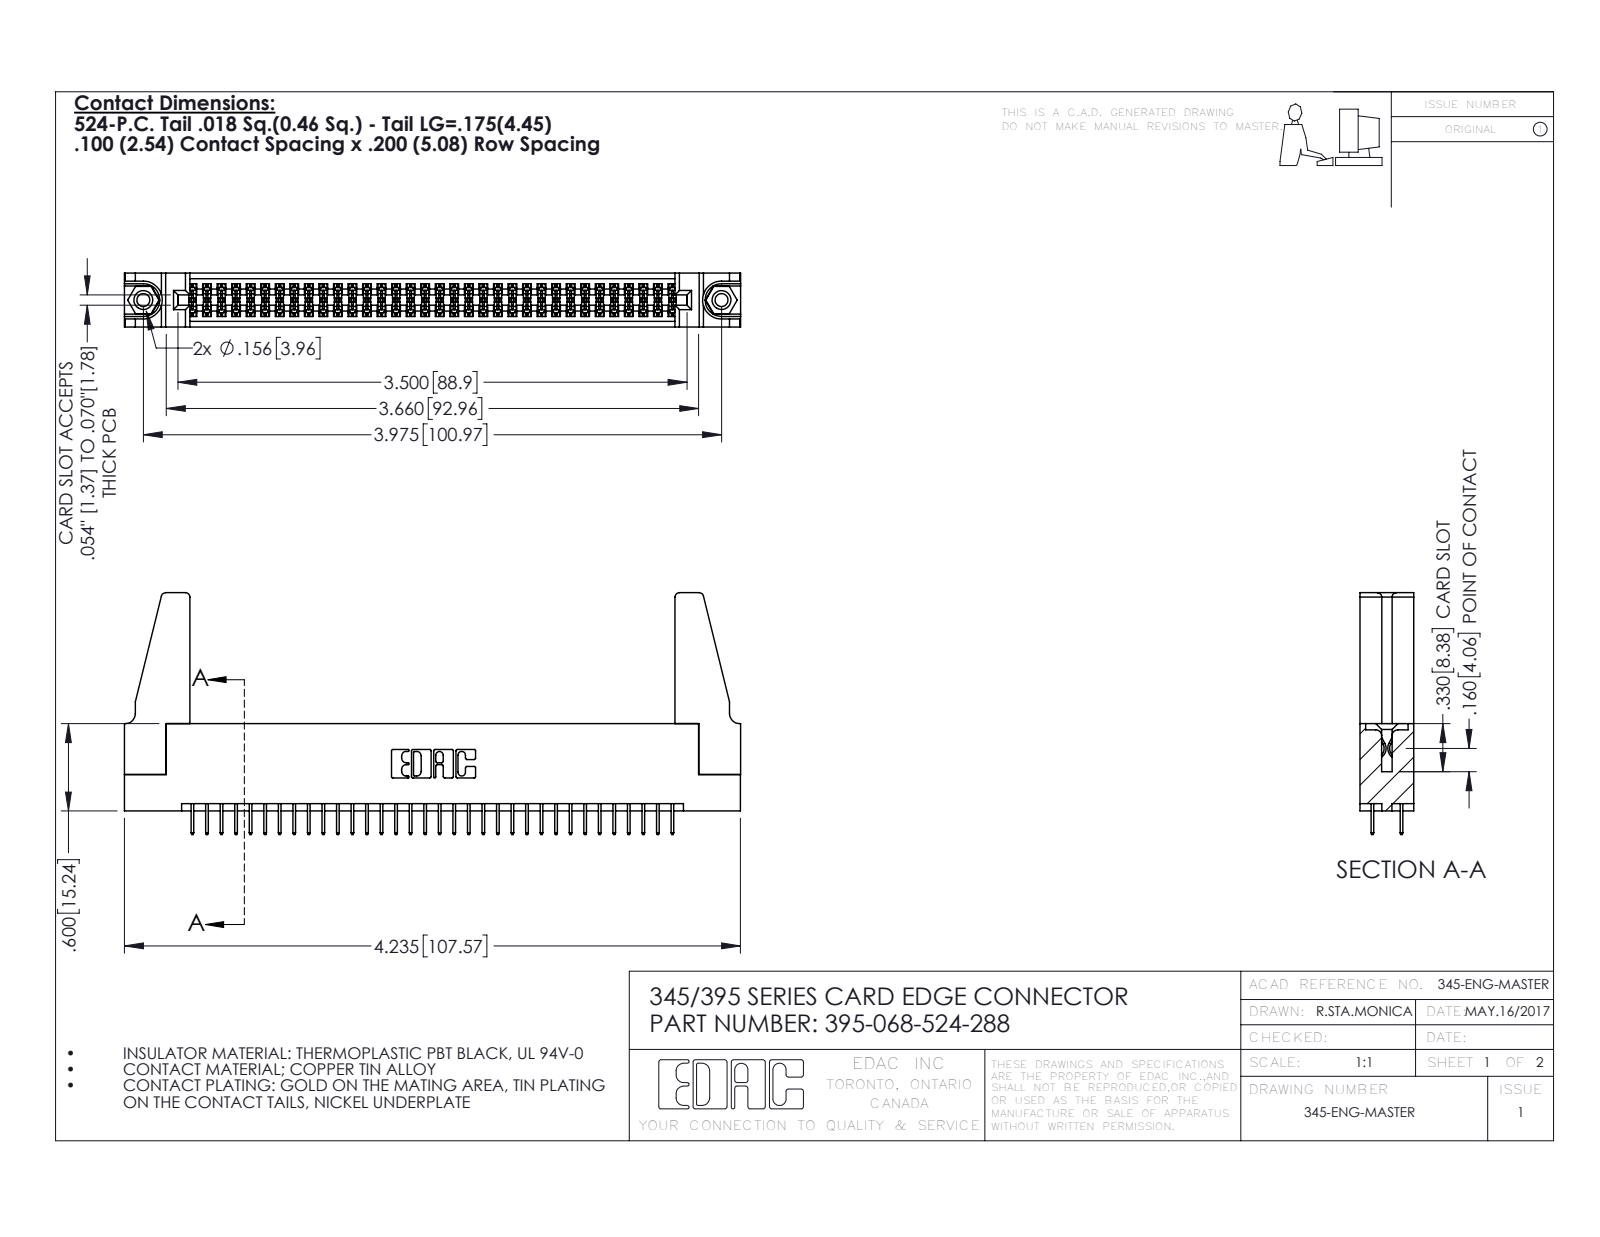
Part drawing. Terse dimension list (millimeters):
name: 395-068-524-288; 345 Part_Flush Mounting Lugs - 0.156 Dia-TH; 345-250-001_345-250-001-102; 345-292-001_345-293-124 (+1 more)
written by: SolidWorks 2016 (CONFIG_CONTROL_DESIGN)
unit: mm
bodies: 73 solids, 3922 faces (2804 planar, 1102 cylindrical, 16 other)
size: 107.6 × 42.2 × 9.4
volume: 13 500 mm³; area: 17 880 mm²
holes: 2× ⌀2.3, 2× ⌀3.2, 2× ⌀4, 1× ⌀1.6
bosses: 2× ⌀3.9
rounds: 102× R0.2, 22× R0.3, 8× R0.8, 6× R0.2, 6× R0.8, 3× R0.7, 2× R0.4, 2× R0.5
face distances: 1.8, 7.6, 9.4, 5.1, 2.5, 6.9, 0.6, 5.7, 1.8, 4.4
hole spacings: 6.9, 95, 101
